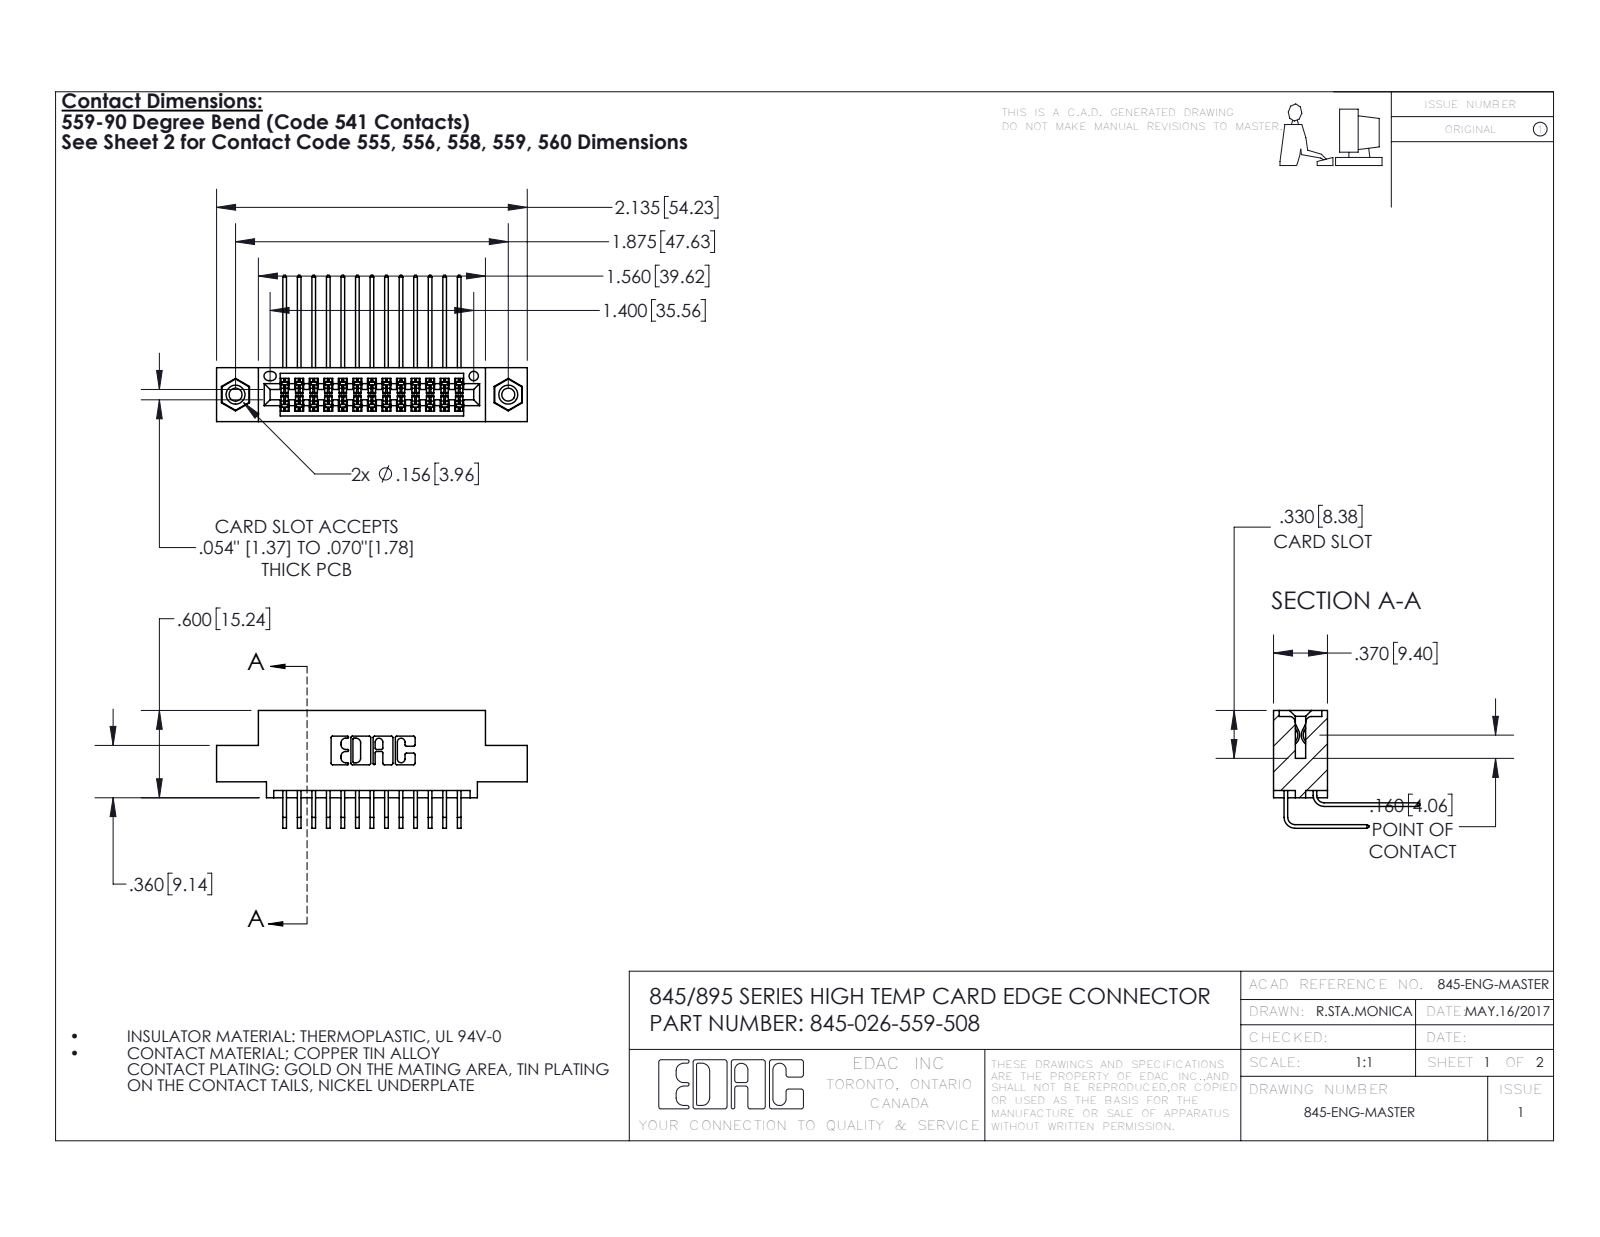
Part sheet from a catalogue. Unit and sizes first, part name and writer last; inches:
Units: inches
Overall size (bounding box): 2.135 × 1.005 × 0.809
Round holes (diameter × count): ⌀0.089 ×2, ⌀0.125 ×2, ⌀0.156 ×2, ⌀0.064 ×1
Round bosses / shafts (diameter × count): ⌀0.155 ×2
Partial cylindrical surfaces — rounded edges, fillets, slot ends (radius × count): R0.006 ×39, R0.01 ×22, R0.007 ×6, R0.031 ×6, R0.026 ×3, R0.014 ×2, R0.019 ×2, R0.022 ×2
Main face-to-face distances: 0.072, 0.298, 0.2, 0.37, 0.098, 0.272, 0.025, 0.225, 0.15, 0.1
Hole centre spacings: 0.27, 1.643, 1.875
Volume: 0.309 in³ · Surface area: 12 in²
Bodies: 29 solids, 1542 faces (1026 planar, 500 cylindrical, 16 other)
Part name (STEP PRODUCT): 345-250-001_345-250-003-102; 345-292-001_558 559 Tail - 1; 345-292-001_559 Tail - 2; 345-026-559-508 (+1 more)
STEP written by: SolidWorks 2016 (CONFIG_CONTROL_DESIGN)
